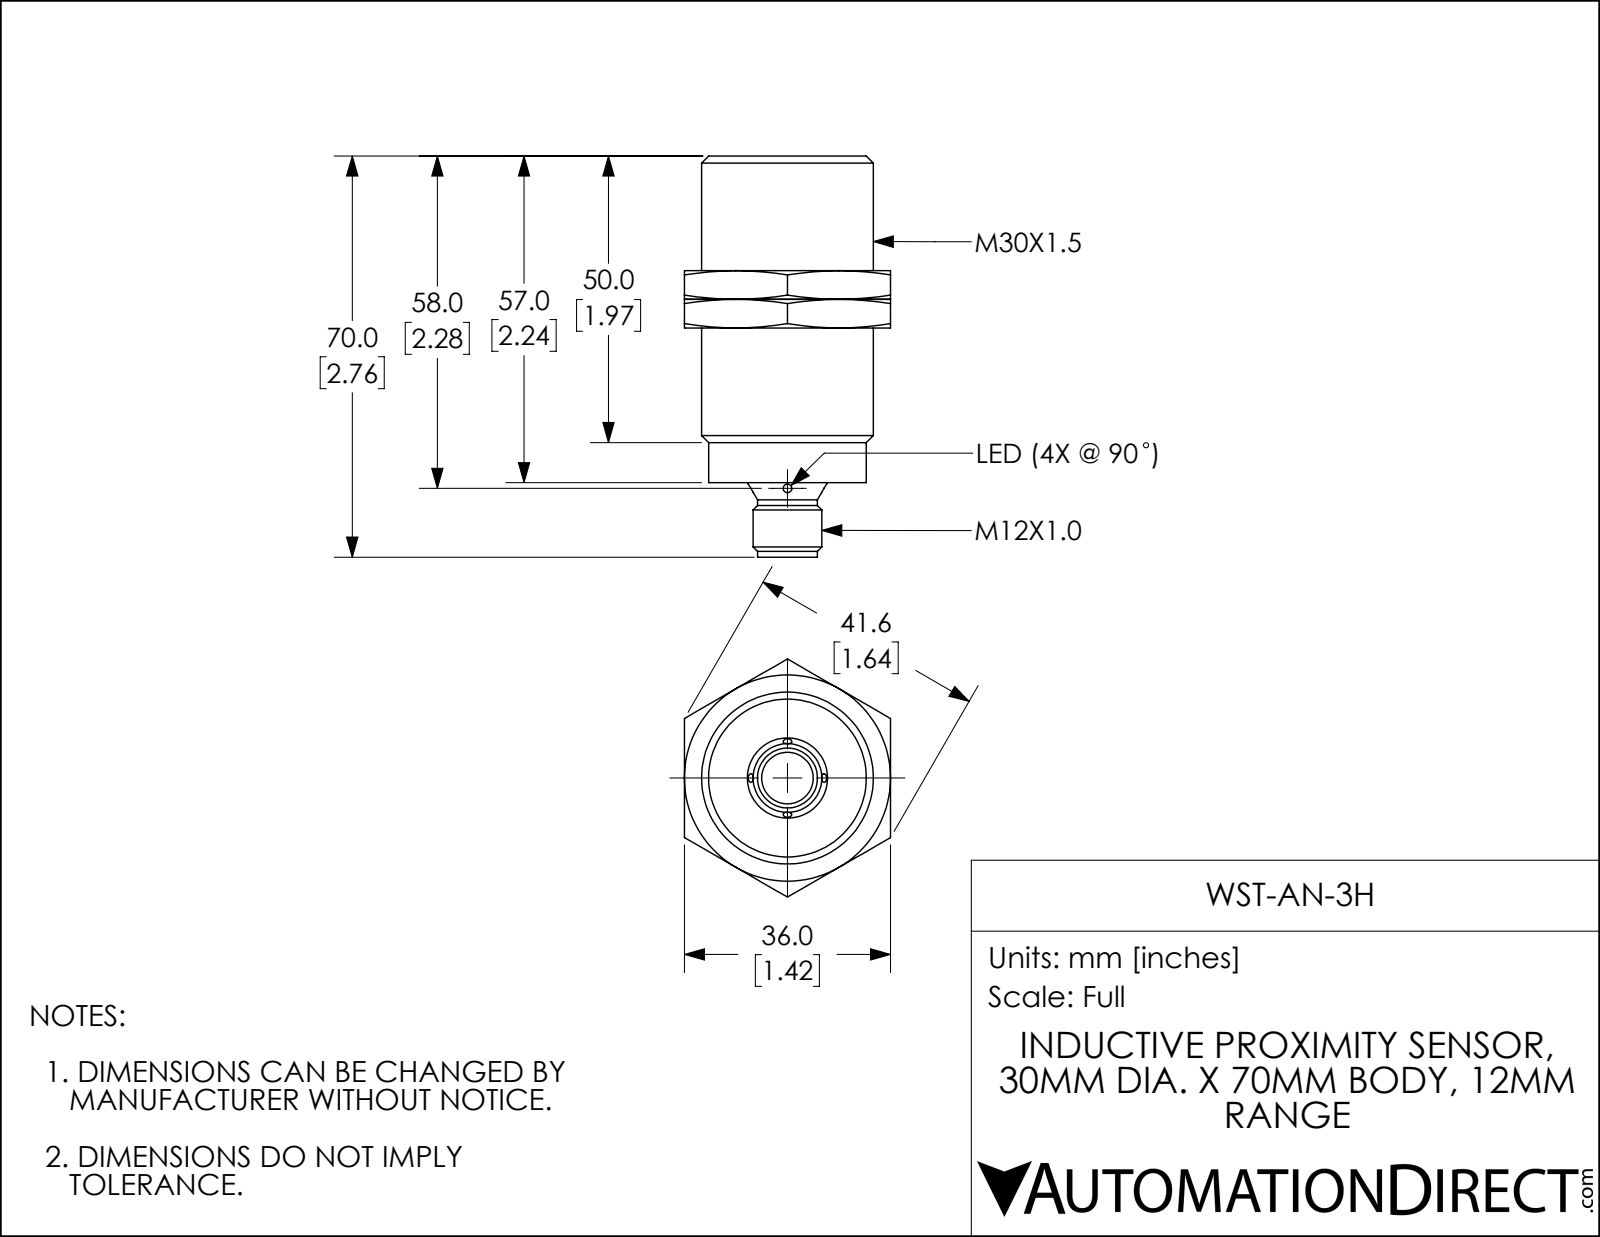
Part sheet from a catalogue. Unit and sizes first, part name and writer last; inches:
Units: inches
Overall size (bounding box): 2.756 × 1.637 × 1.417
Round holes (diameter × count): ⌀0.059 ×2, ⌀0.354 ×1, ⌀1.084 ×1, ⌀1.117 ×1
Round bosses / shafts (diameter × count): ⌀1.181 ×1, ⌀0.472 ×1, ⌀0.412 ×1
Partial cylindrical surfaces — rounded edges, fillets, slot ends (radius × count): R0.228 ×1
Main face-to-face distances: 0.197, 0.984, 1.417, 1.26, 2.244, 1.457, 0.787, 1.063, 0.394, 1.181
Volume: 2.747 in³ · Surface area: 17.21 in²
Bodies: 3 solids, 71 faces (20 planar, 17 cylindrical, 34 other)
Part name (STEP PRODUCT): WST-AN-3H
STEP written by: SolidWorks 2017 (AUTOMOTIVE_DESIGN)
